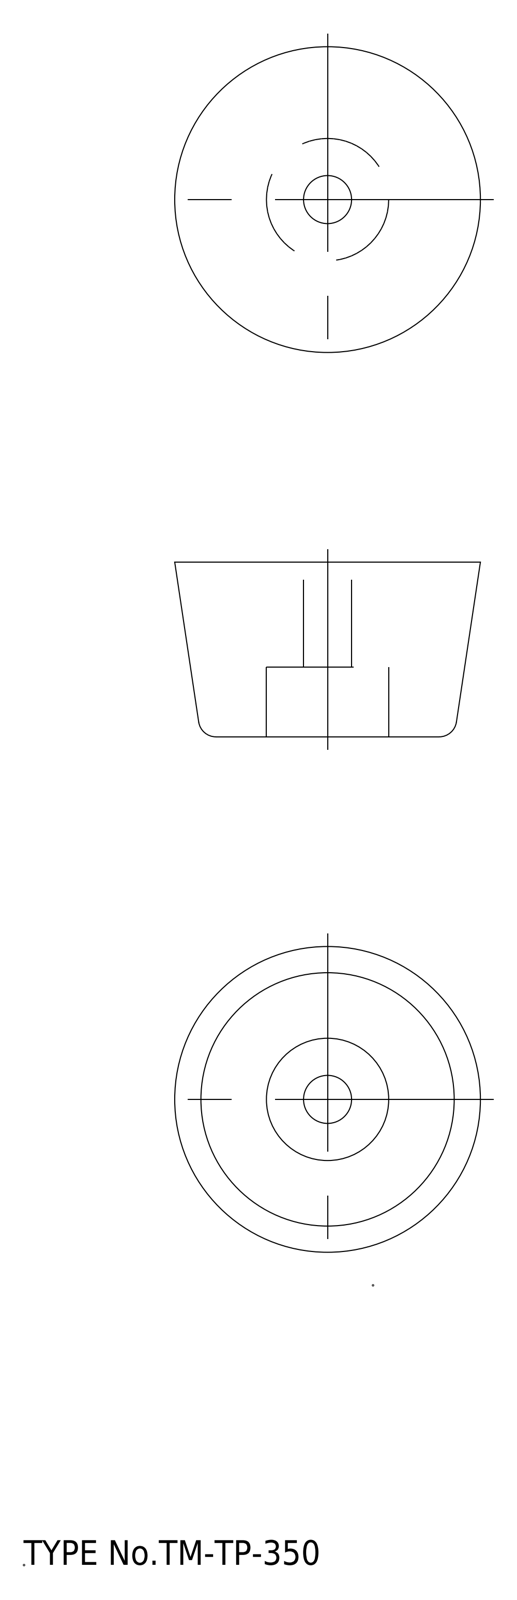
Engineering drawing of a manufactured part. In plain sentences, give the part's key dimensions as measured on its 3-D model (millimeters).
Its 3-D file was written by "spGate 19.8.4 (****-****-****-****) (AUTOMOTIVE_DESIGN)". It is 1 solid with 11 faces: 3 planar, 4 cylindrical and 4 other. Overall it measures 35 by 35 by 20 millimeters. Its volume is 14 593 cubic millimeters and its surface area 4 114 square millimeters. Round holes: 1 of diameter 5.5, 1 of diameter 14. The main face-to-face distances are 20, 8, 12.
